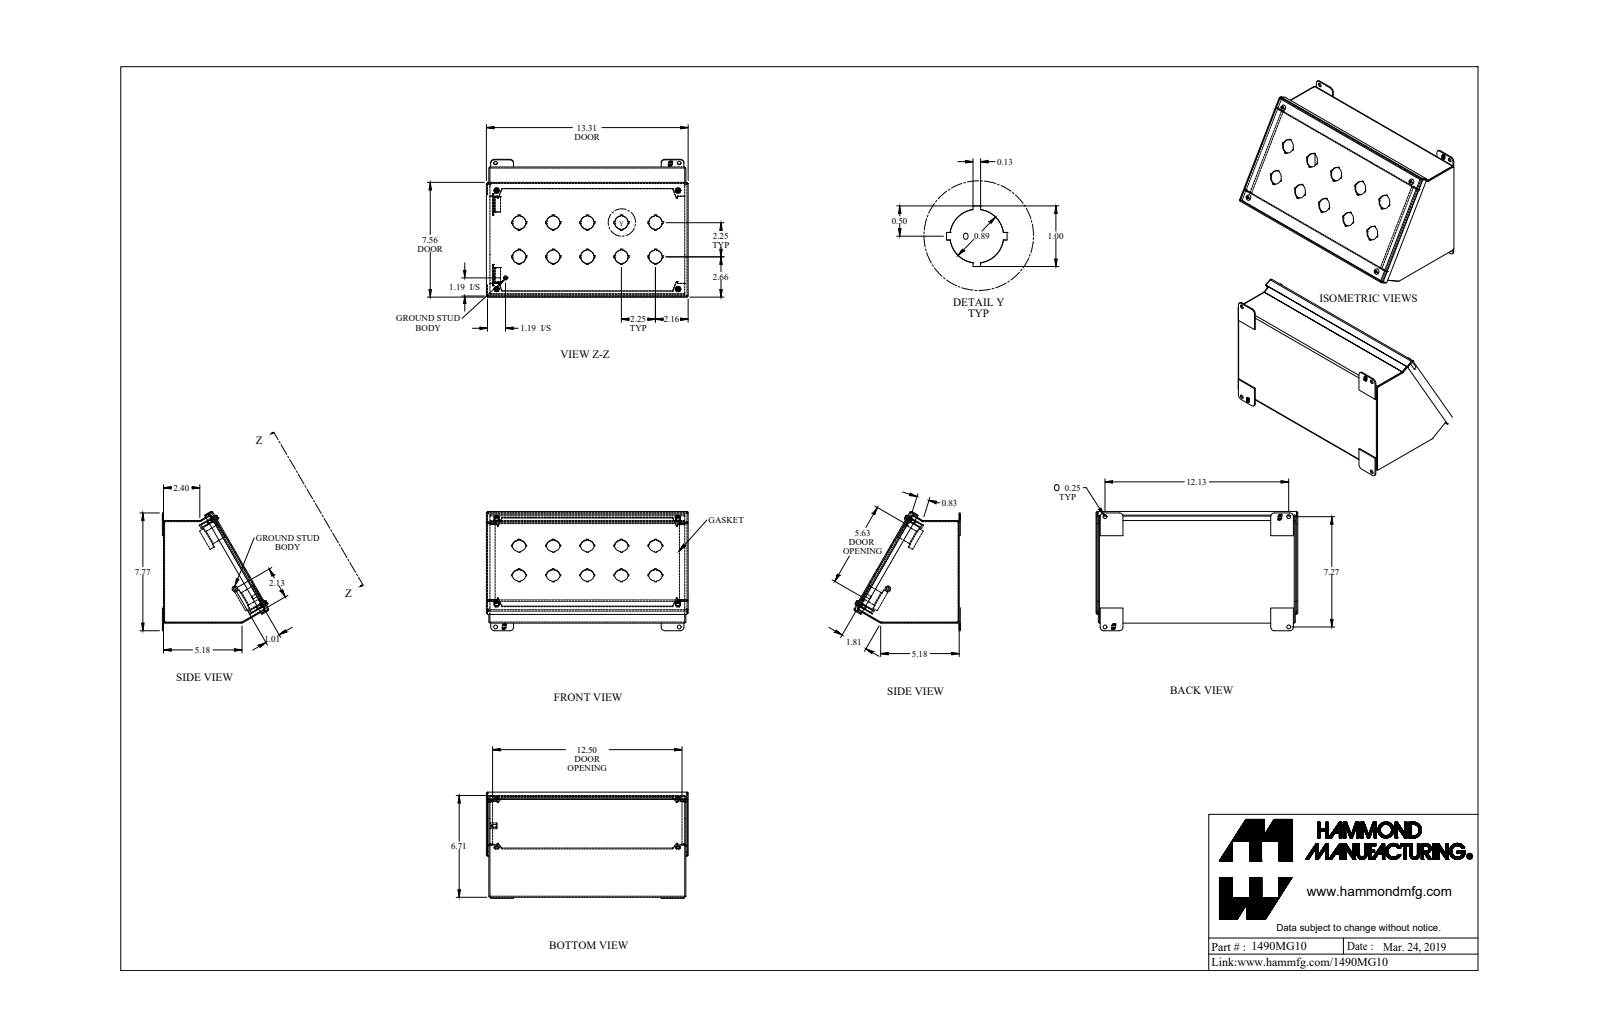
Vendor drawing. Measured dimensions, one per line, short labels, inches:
name: 1490MG10_Default
written by: SolidWorks 2019 (CONFIG_CONTROL_DESIGN)
unit: in
bodies: 26 solids, 854 faces (603 planar, 213 cylindrical, 38 other)
size: 13.312 × 7.891 × 7.053
volume: 30.31 in³; area: 863.8 in²
holes: 8× ⌀0.25, 5× ⌀0.875, 5× ⌀0.875, 4× ⌀0.159, 1× ⌀0.12, 1× ⌀0.136, 1× ⌀0.156
bosses: 4× ⌀0.39, 4× ⌀0.275, 4× ⌀0.19, 4× ⌀0.148, 1× ⌀0.375, 1× ⌀0.29
rounds: 18× R0.108, 12× R0.036, 8× R0.029, 8× R0.086, 8× R0.25, 4× R0.125, 4× R0.16, 4× R0.171
face distances: 0.072, 12.928, 6.698, 12.856, 13, 6.77, 6.626, 7.334, 0.072, 0.156
hole spacings: 2.25, 3.182, 4.5, 5.031, 5.749, 7.409, 8.5, 9.32
